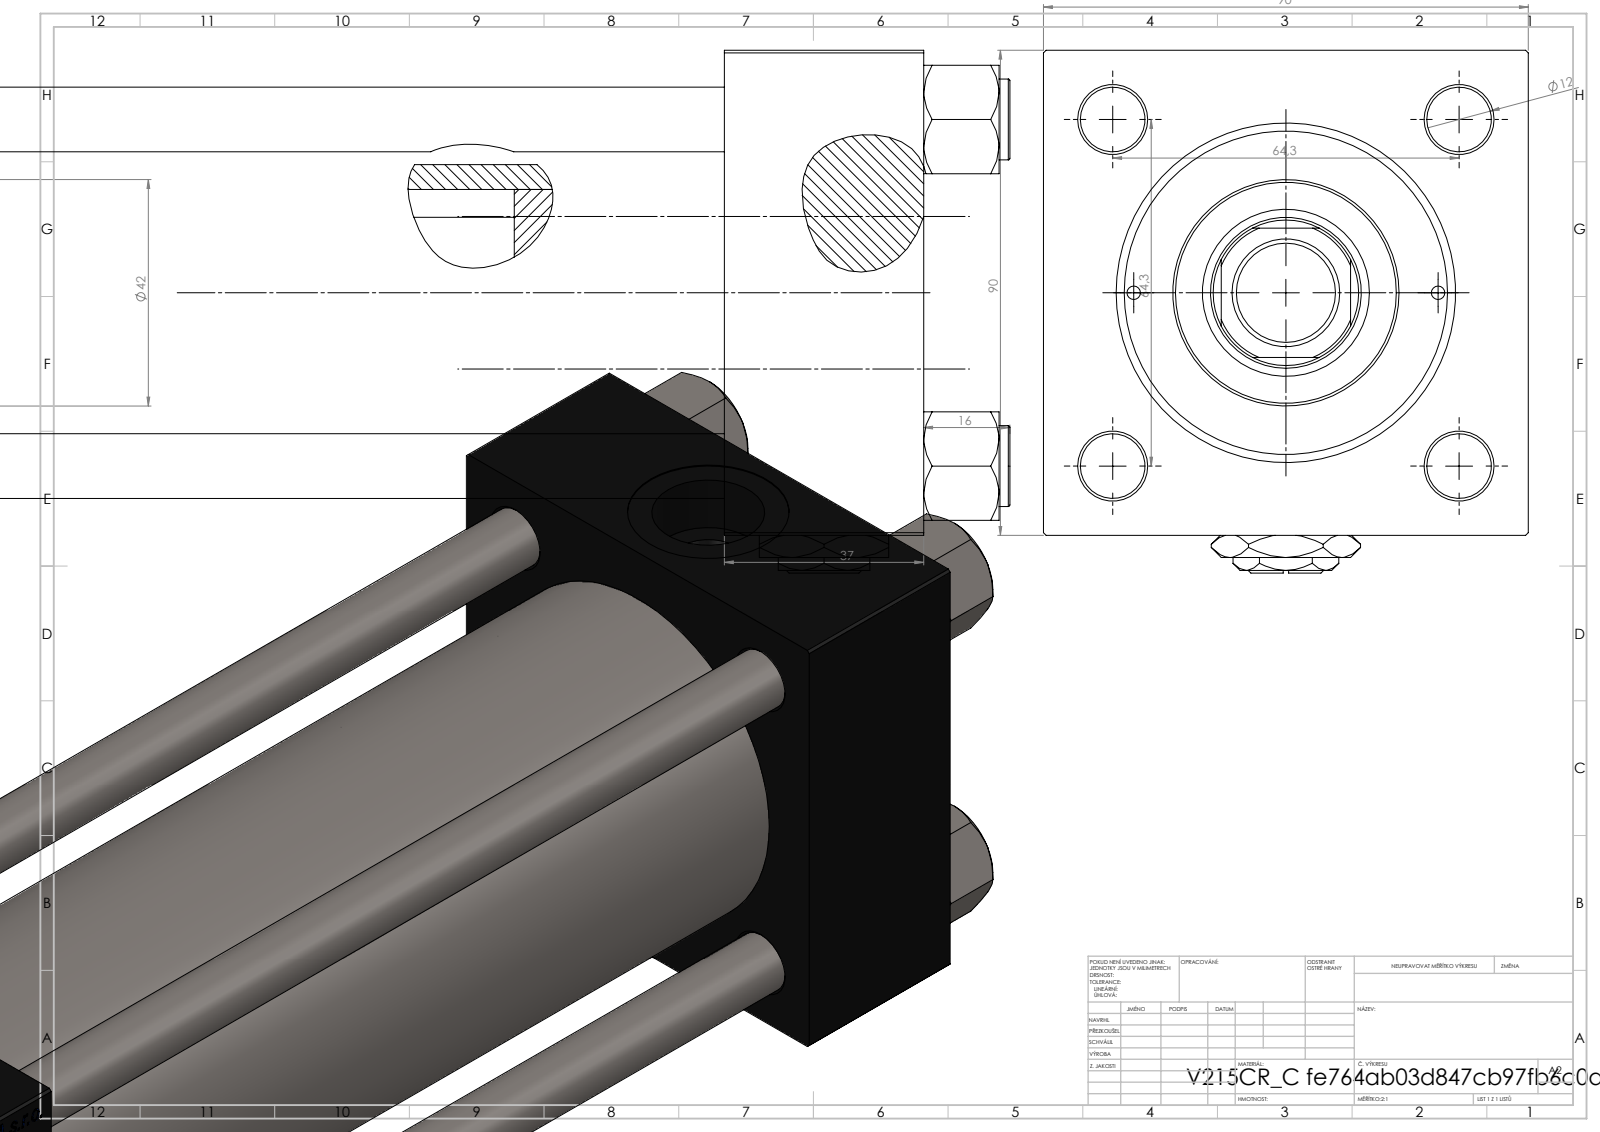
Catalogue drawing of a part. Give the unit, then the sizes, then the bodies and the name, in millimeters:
Units: millimetres
Overall size (bounding box): 371 × 97 × 90
Round holes (diameter × count): ⌀12 ×4, ⌀2.5 ×2, ⌀7 ×2, ⌀20.96 ×2, ⌀30 ×2, ⌀18.5 ×1, ⌀28 ×1, ⌀31 ×1, ⌀50 ×1, ⌀60 ×1, ⌀63 ×1
Round bosses / shafts (diameter × count): ⌀15 ×4, ⌀69 ×1, ⌀42 ×1, ⌀20 ×1, ⌀18 ×1
Partial cylindrical surfaces — rounded edges, fillets, slot ends (radius × count): R13.5 ×1
Main face-to-face distances: 90, 37, 258, 295, 59, 236, 199, 266.3, 229.3, 30.3
Hole centre spacings: 32.39, 45.47, 64.3, 68.42, 28.25, 90.93, 56.5, 237.5
Volume: 1 185 000 mm³ · Surface area: 278 027 mm²
Bodies: 14 solids, 1270 faces (580 planar, 106 cylindrical, 584 other)
Part name (STEP PRODUCT): V215CR_C_TYCINKA; V215_VC_A; ROD_END_AH; V215CR_VCP_C (+3 more)
STEP written by: SolidWorks 2019 (CONFIG_CONTROL_DESIGN)
